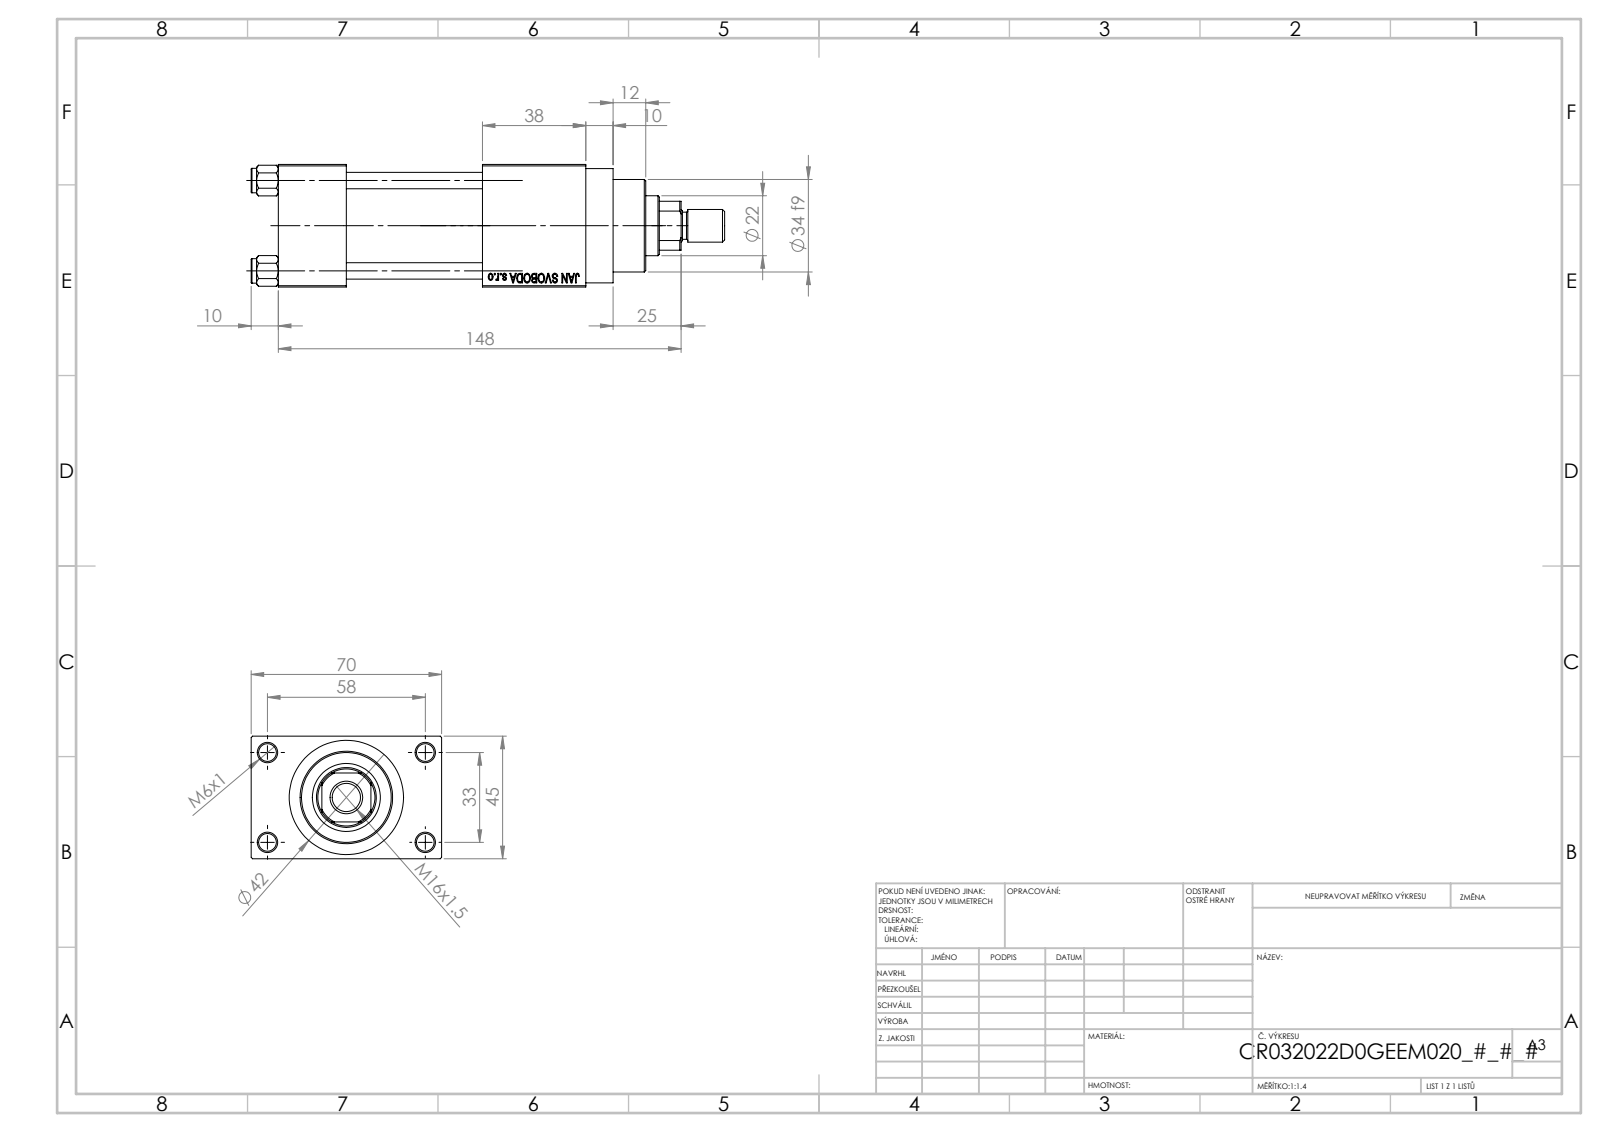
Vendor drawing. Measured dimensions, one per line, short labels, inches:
name: V215CR_VCP_D; V215CR_D_TYCINKA; V215_VC_A; ROD_END_E (+2 more)
written by: SolidWorks 2019 (CONFIG_CONTROL_DESIGN)
unit: in
bodies: 12 solids, 1117 faces (500 planar, 93 cylindrical, 524 other)
size: 6.85 × 2.756 × 1.772
volume: 15.03 in³; area: 124.5 in²
holes: 4× ⌀0.236, 4× ⌀0.256, 2× ⌀0.276, 2× ⌀0.518, 2× ⌀0.787, 1× ⌀0.413, 1× ⌀0.866, 1× ⌀0.945, 1× ⌀0.984, 1× ⌀1.26, 1× ⌀1.299
bosses: 4× ⌀0.354, 1× ⌀1.654, 1× ⌀1.496, 1× ⌀1.339, 1× ⌀0.472, 1× ⌀0.394
rounds: 1× R0.413
face distances: 1.772, 0.984, 0.492, 2.264, 1.969, 2.953, 3.465, 2.756, 1.496, 4.449
hole spacings: 0.488, 0.924, 1.307, 1.314, 1.392, 1.795, 2.219, 1.299
